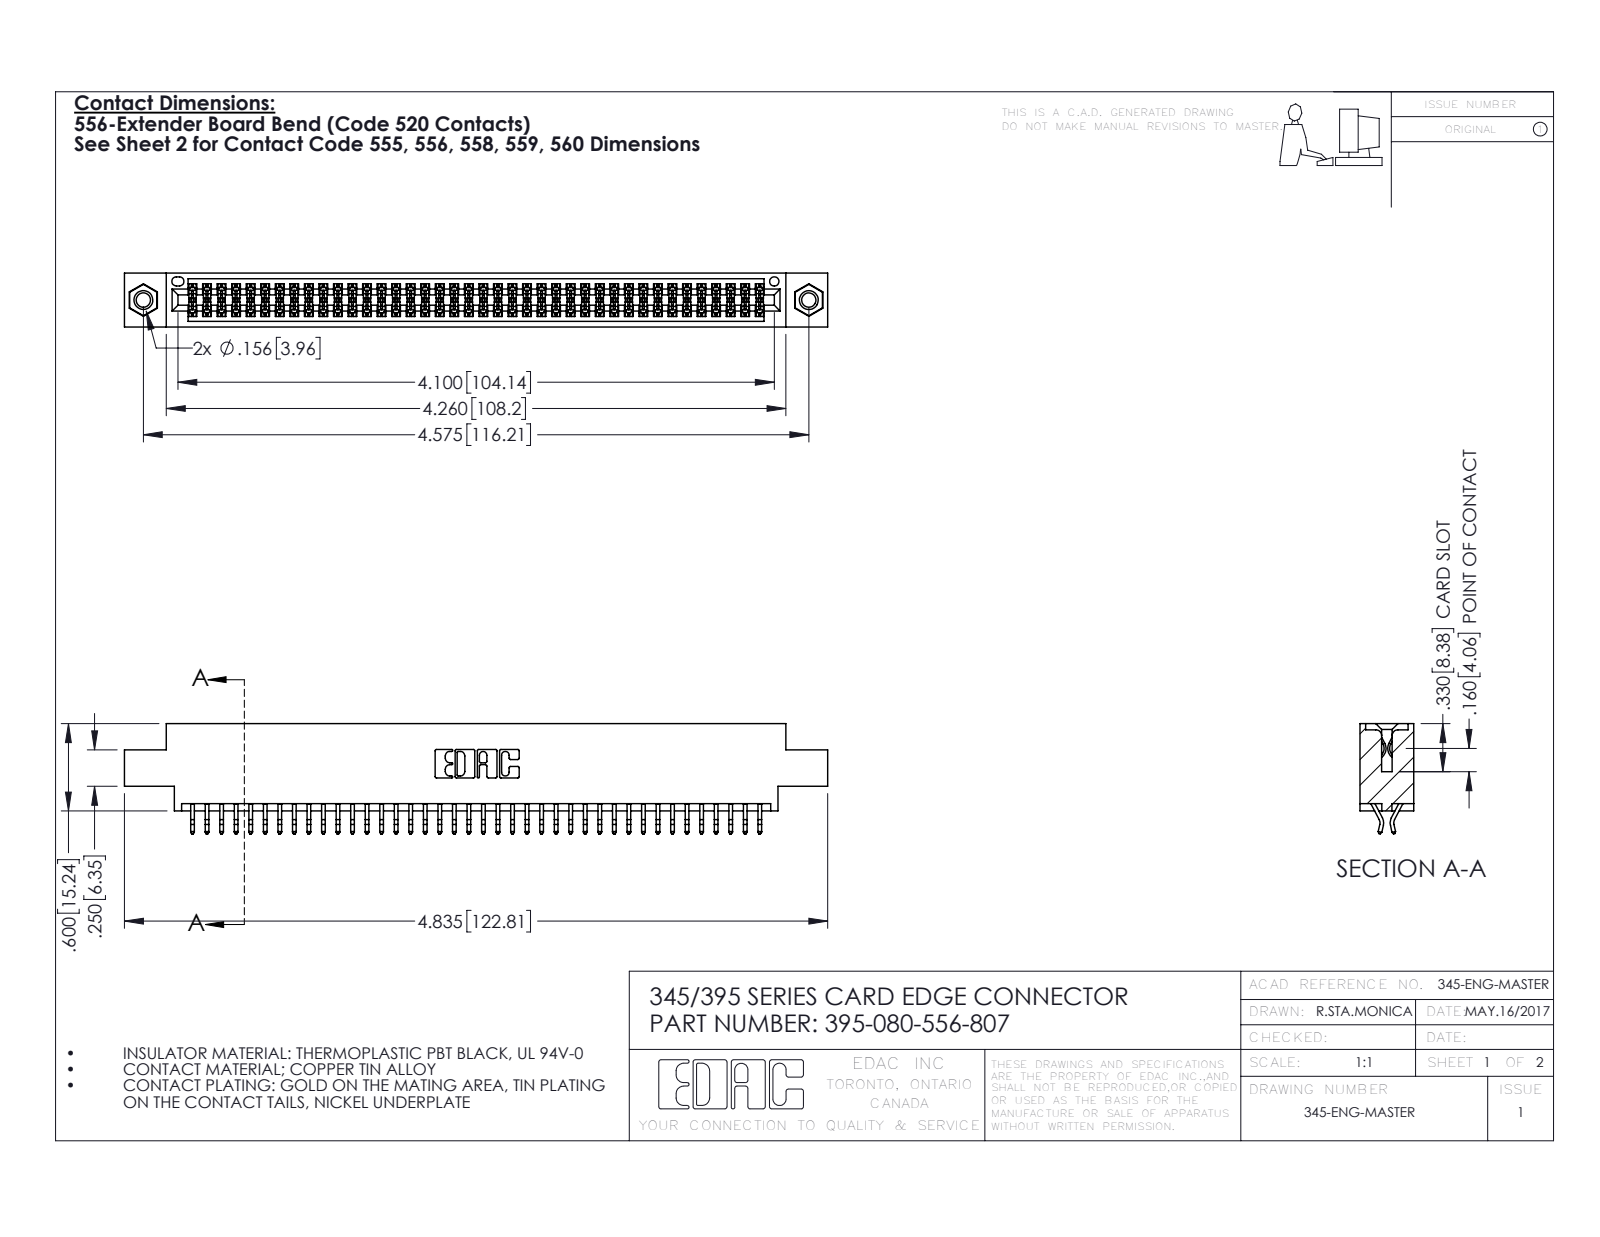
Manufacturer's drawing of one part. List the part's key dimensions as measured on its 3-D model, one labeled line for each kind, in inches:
Part name (STEP PRODUCT): 345-292-001_556 Tail; 395-080-556-807; 345 Part_0.170 Offset - 0.156 Dia-TI; 345-250-001_345-250-005-103
STEP written by: SolidWorks 2016 (CONFIG_CONTROL_DESIGN)
Units: inches
Bodies: 83 solids, 4670 faces (3076 planar, 1578 cylindrical, 16 other)
Overall size (bounding box): 4.835 × 0.757 × 0.37
Volume: 0.719 in³ · Surface area: 27.09 in²
Round holes (diameter × count): ⌀0.098 ×2, ⌀0.125 ×2, ⌀0.156 ×2, ⌀0.064 ×1
Round bosses / shafts (diameter × count): ⌀0.155 ×2
Partial cylindrical surfaces — rounded edges, fillets, slot ends (radius × count): R0.006 ×120, R0.01 ×22, R0.007 ×6, R0.031 ×6, R0.026 ×3, R0.01 ×2, R0.014 ×2, R0.019 ×2
Main face-to-face distances: 0.072, 0.298, 0.37, 0.2, 0.025, 0.098, 0.272, 0.225, 0.175, 0.149
Hole centre spacings: 0.27, 4.339, 4.575
